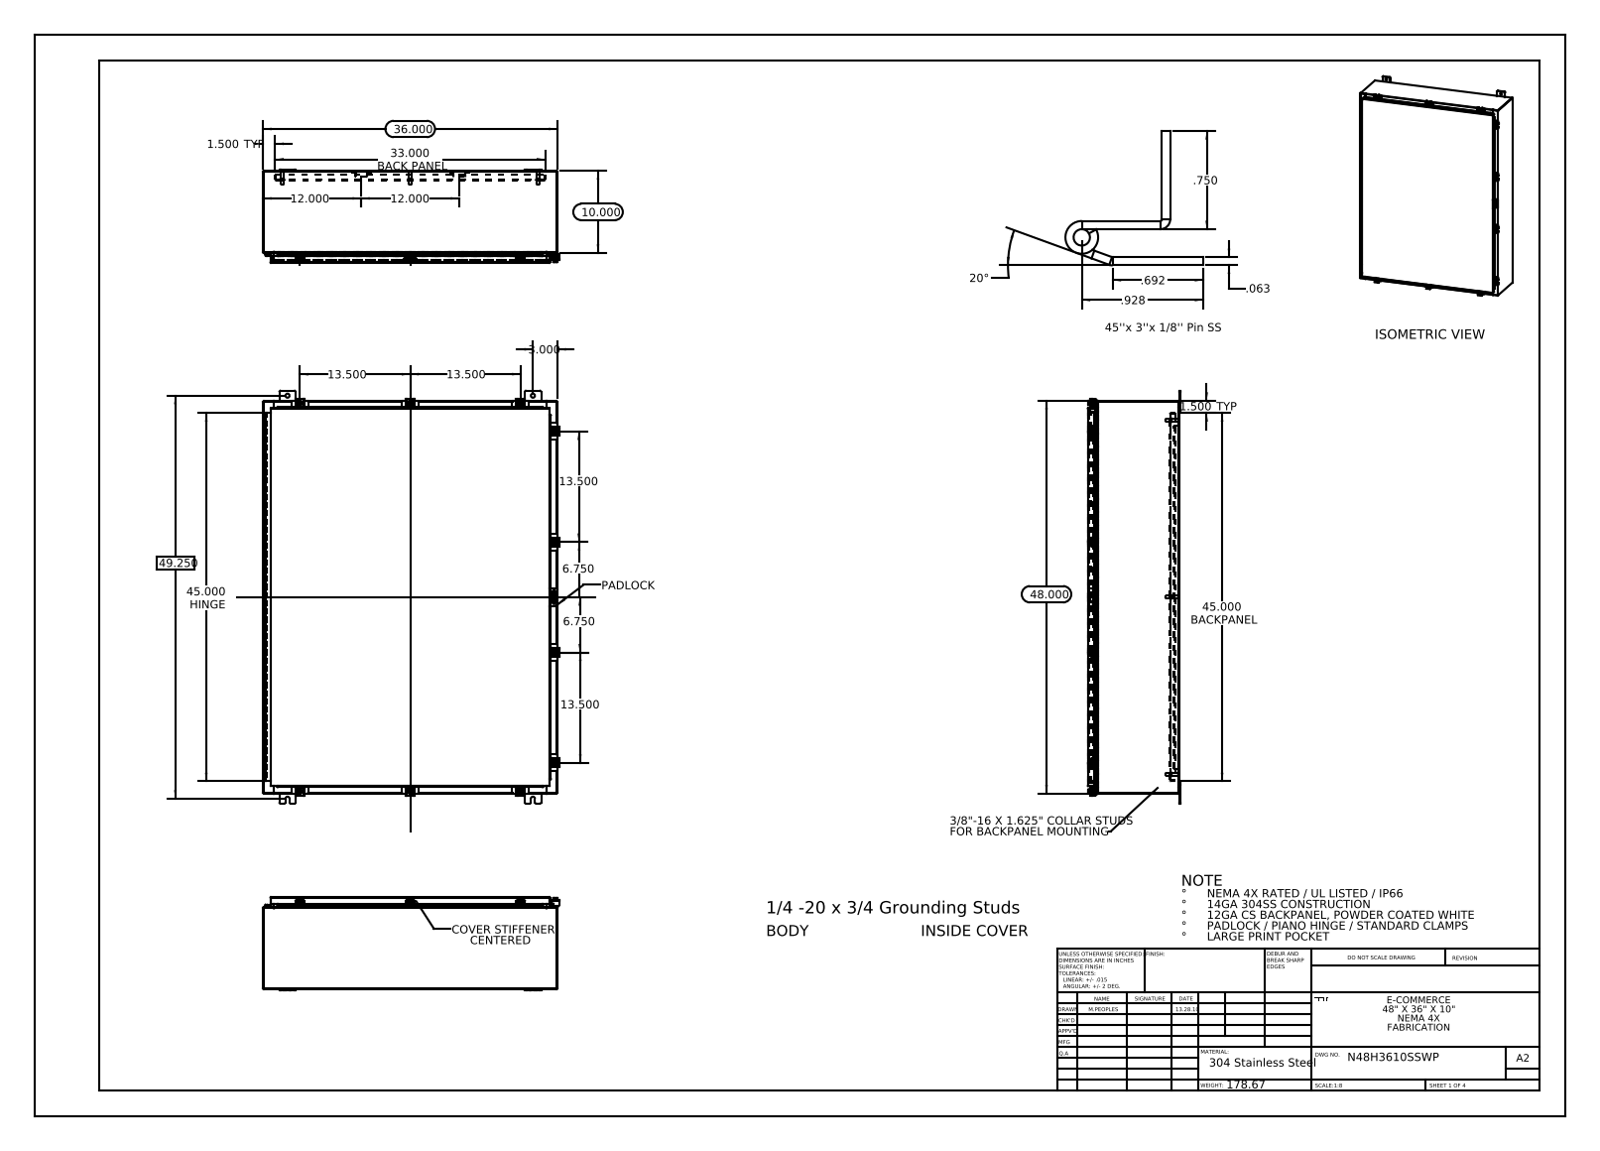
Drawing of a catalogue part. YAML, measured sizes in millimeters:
part_name: "N48H3610SSWP Clamp Top; N48H3610SSWP Door Stiffener; N48H3610SSWP Padlock Hasp; N48H3610SSWP (+8 more)"
step_written_by: "SolidWorks 2013 (CONFIG_CONTROL_DESIGN)"
units: millimeters
bodies: {solids: 74, faces: 2999, planar: 1562, cylindrical: 1269, other: 168}
overall_size: [1282.7, 919.8, 289.3]
volume: 10260000
surface_area: 10060000
round_holes:
  - {diameter: 12.7, count: 12}
  - {diameter: 5.4, count: 10}
  - {diameter: 6.6, count: 10}
  - {diameter: 6.4, count: 6}
  - {diameter: 3.2, count: 2}
  - {diameter: 3.2, count: 1}
round_bosses_or_shafts:
  - {diameter: 6.4, count: 11}
  - {diameter: 12.7, count: 10}
  - {diameter: 10.1, count: 10}
  - {diameter: 15.9, count: 8}
  - {diameter: 9.5, count: 8}
  - {diameter: 8.4, count: 8}
partial_cylinders:
  - {radius: 1.5, count: 46}
  - {radius: 0.3, count: 39}
  - {radius: 2.2, count: 33}
  - {radius: 4.8, count: 24}
  - {radius: 3, count: 20}
  - {radius: 3.6, count: 20}
  - {radius: 1.3, count: 15}
  - {radius: 2, count: 14}
face_to_face_distances: [1.9, 282.6, 280.7, 2.6, 284.5, 25.4, 257.2, 27.3, 255.3, 29.9]
hole_center_spacings: [342.9, 347, 508, 511.1, 549.3, 605, 685.8, 965.3]
